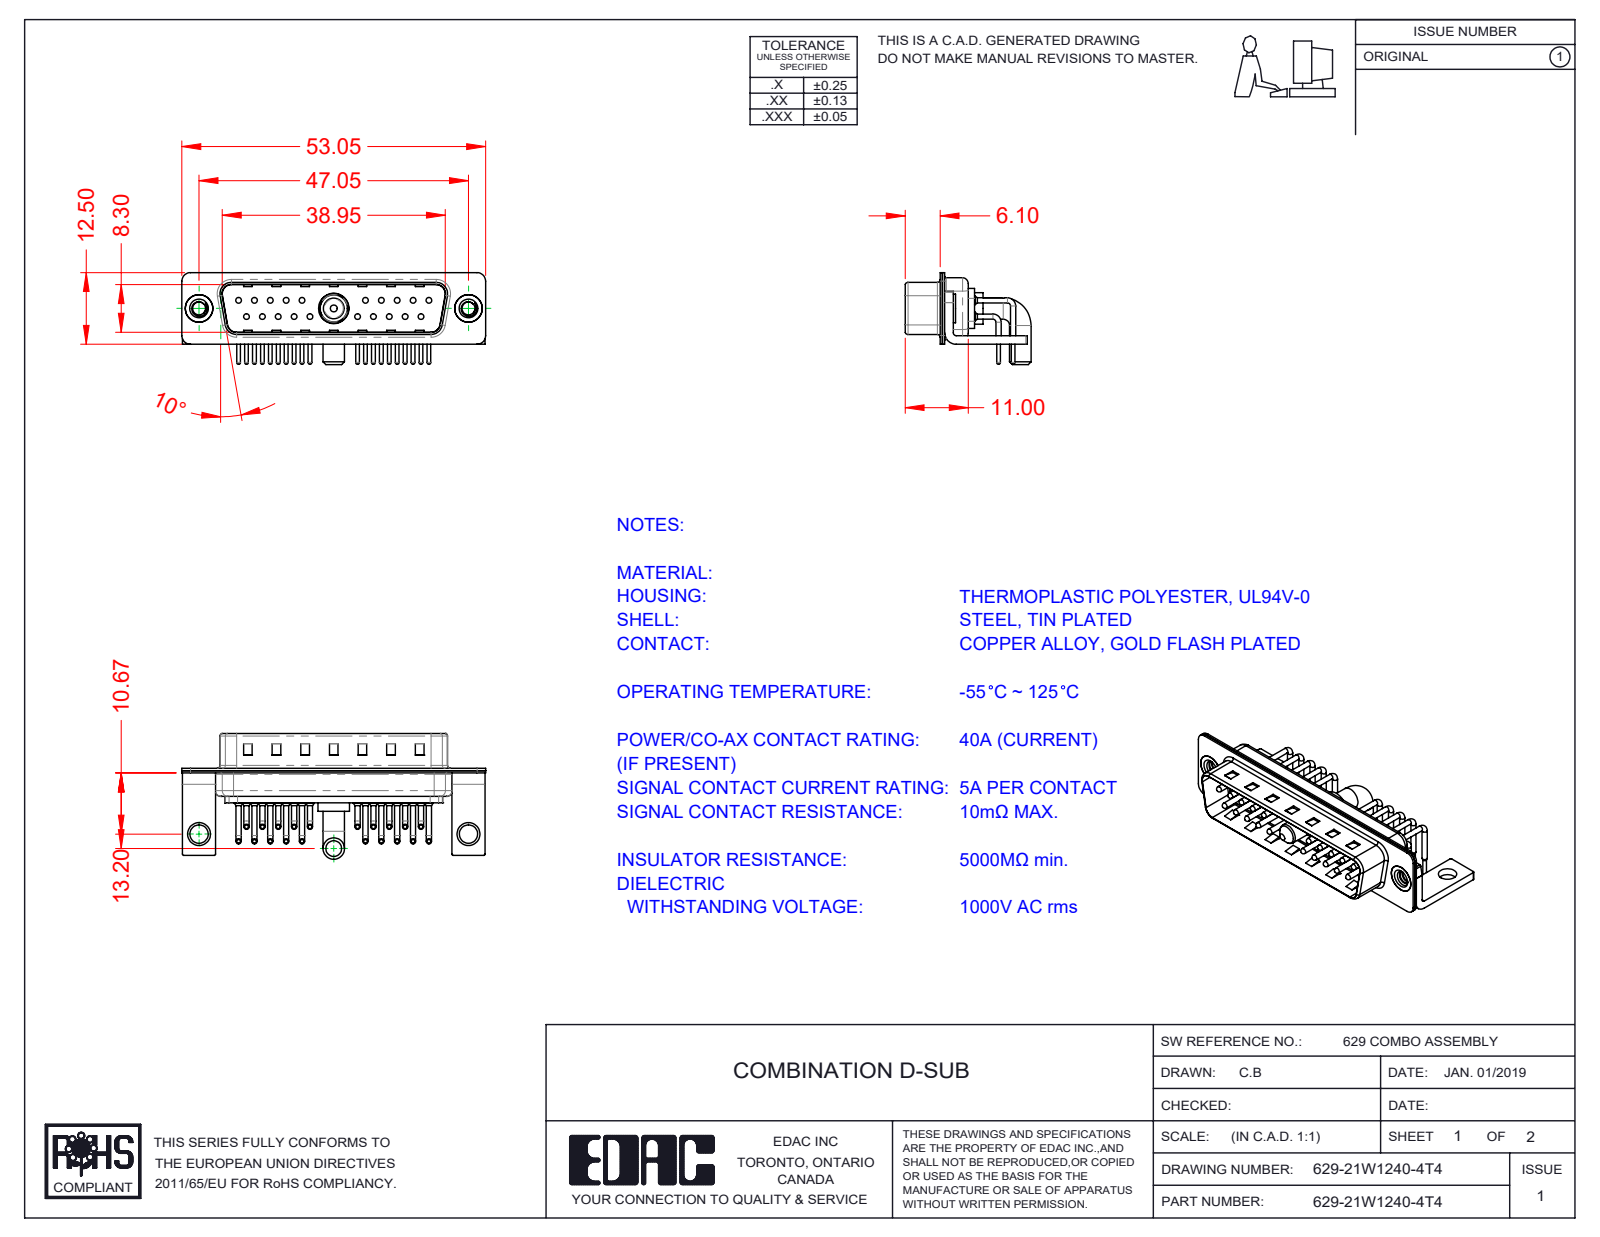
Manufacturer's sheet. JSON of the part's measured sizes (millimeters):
{"part_name": "629Combo Contact Row 1; 629-21W1240-4T4; 629Combo Contact Row 2; Power Pin_40A RA (+5 more)", "step_written_by": "SolidWorks 2020 (CONFIG_CONTROL_DESIGN)", "units": "millimeters", "bodies": {"solids": 29, "faces": 2659, "planar": 1481, "cylindrical": 896, "other": 282}, "overall_size": [53.05, 21.98, 16.05], "volume_mm3": 3358, "surface_area_mm2": 8226, "round_holes": [[0.75, 20], [1.6, 20], [2, 20], [2.26, 2], [3.2, 2], [4, 2], [4.8, 2], [4.85, 1], [5.3, 1]], "round_bosses_or_shafts": [[0.9, 40], [1.5, 20], [1, 20], [0.65, 20], [5, 2], [4.9, 2], [3.75, 2], [5.5, 1]], "partial_cylinders_radius": [[1.01, 20], [0.25, 16], [1.5, 16], [2, 13], [0.5, 9], [1.6, 8], [0.6, 4], [0.65, 4]], "face_to_face_distances": [0.4, 0.8, 9.5, 1.5, 9.1, 8.7, 9.9, 0.6, 2.1, 0.75], "hole_center_spacings": [3.16, 2.77, 5.54, 8.31, 5.04, 19.39, 20.97, 22.16]}
